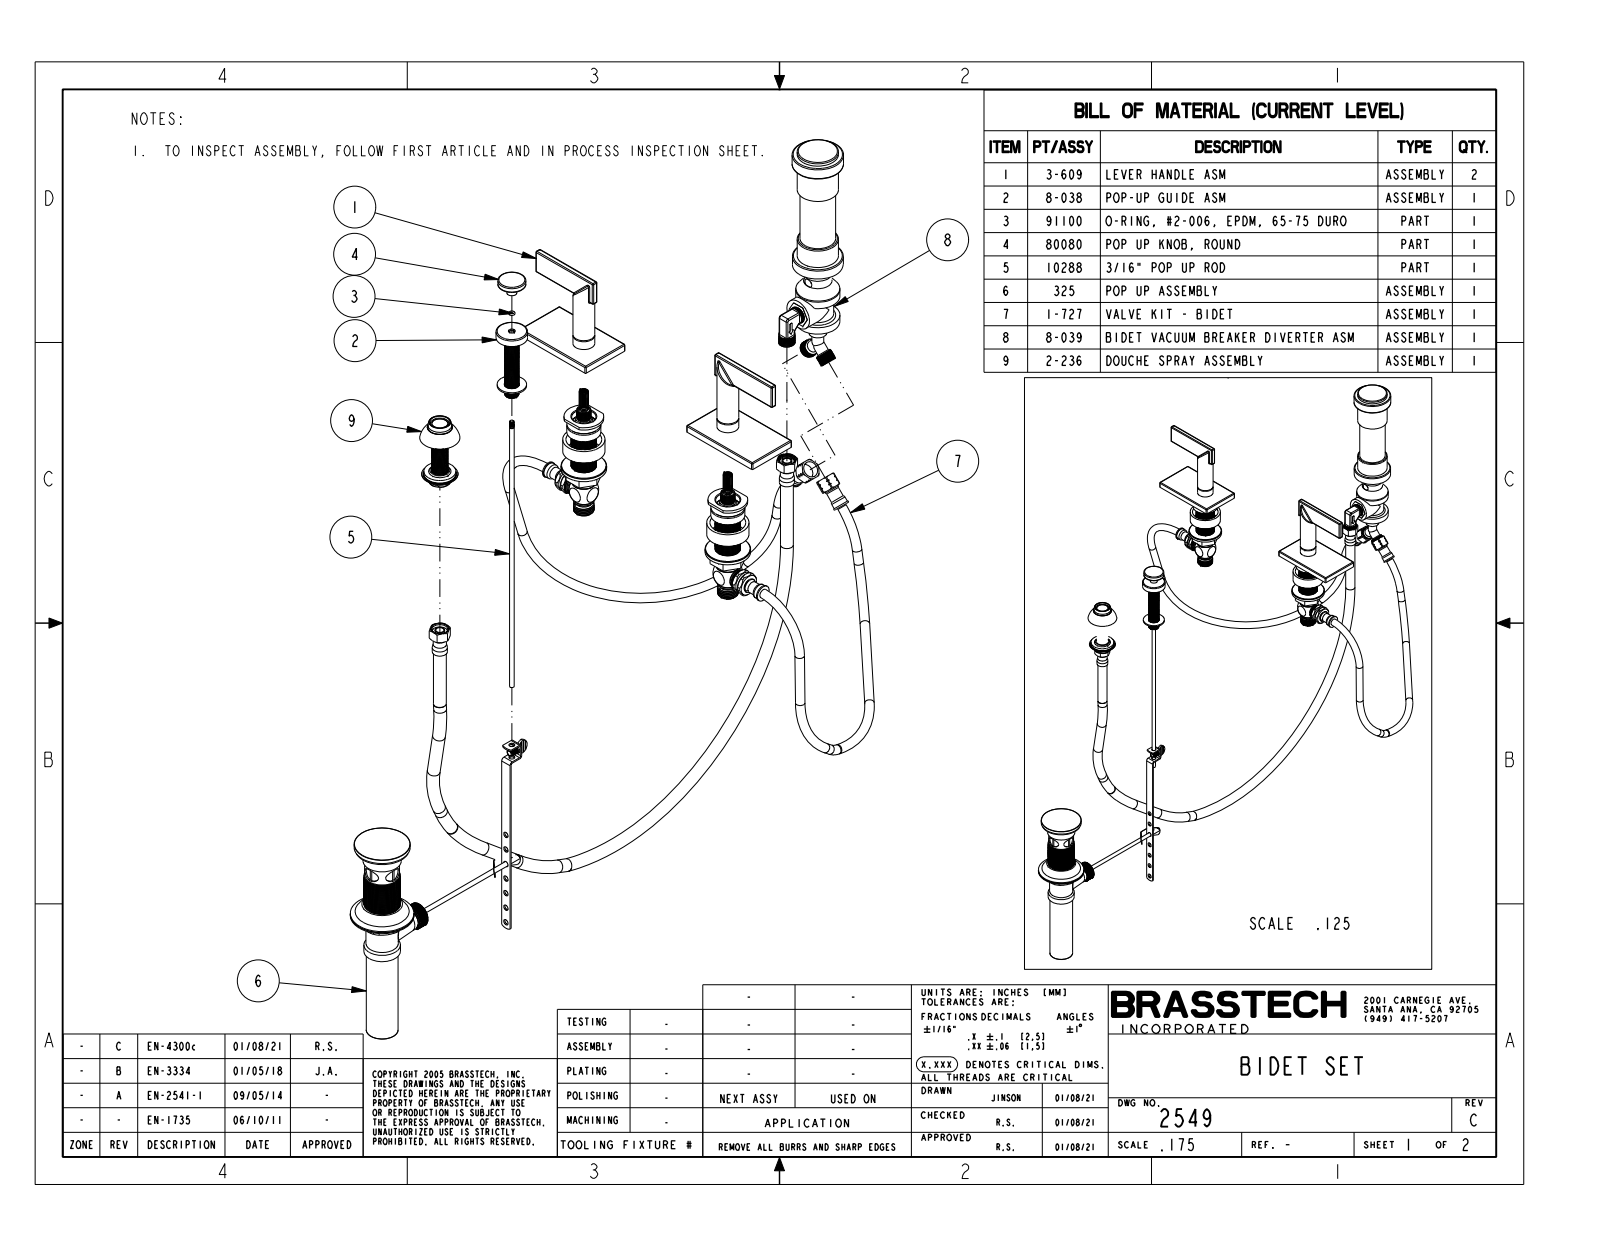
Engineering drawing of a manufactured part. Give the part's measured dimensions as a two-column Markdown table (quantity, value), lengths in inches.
| quantity | value |
| --- | --- |
| part name | 2549 |
| STEP written by | CREO PARAMETRIC BY PTC INC, 2018400 (CONFIG_CONTROL_DESIGN) |
| units | inches |
| bodies | 5 solids, 292 faces (77 planar, 113 cylindrical, 102 other) |
| overall size | 22.8 × 13.12 × 5.445 |
| volume | 21.82 in³ |
| surface area | 119.1 in² |
| round holes (diameter × count) | 0.15 × 1, 0.625 × 1, 0.792 × 1, 0.94 × 1 |
| round bosses / shafts (diameter × count) | 0.86 × 2, 0.68 × 2, 2.02 × 1, 2 × 1, 1.62 × 1, 1.4 × 1, 1.24 × 1, 1.1 × 1 |
| partial cylindrical surfaces (radius × count) | 0.04 × 42, 0.357 × 1 |
| main face-to-face distances | 0.31, 0.236, 0.982, 1.218, 2.2, 5.445, 5.135, 3.66, 9.26, 3.2 |
| hole center spacings | 4 |
